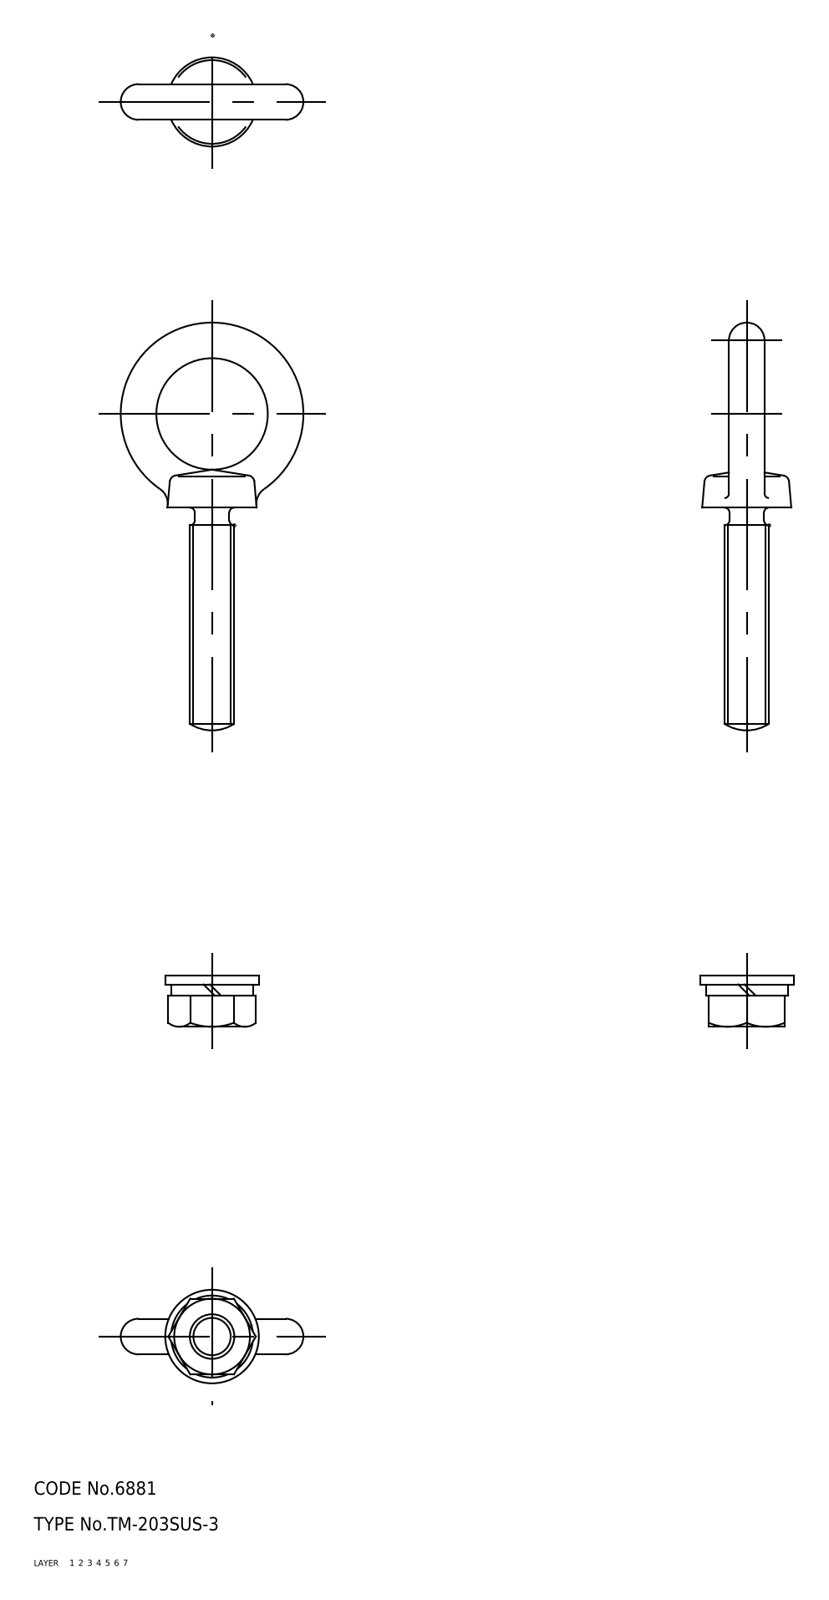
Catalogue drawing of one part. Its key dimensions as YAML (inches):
part_name: "TM_203SUS_3"
step_written_by: "SolidWorks 2003240 (AUTOMOTIVE_DESIGN)"
units: inches
bodies: {solids: 4, faces: 52, planar: 13, cylindrical: 12, other: 27}
overall_size: [3.602, 1.614, 0.827]
volume: 0.776
surface_area: 10.73
round_holes:
  - {diameter: 0.394, count: 1}
round_bosses_or_shafts:
  - {diameter: 0.827, count: 1}
  - {diameter: 0.724, count: 1}
face_to_face_distances: [0.079, 0.098, 0.177, 0.669, 0.276, 0.374, 0.453]
